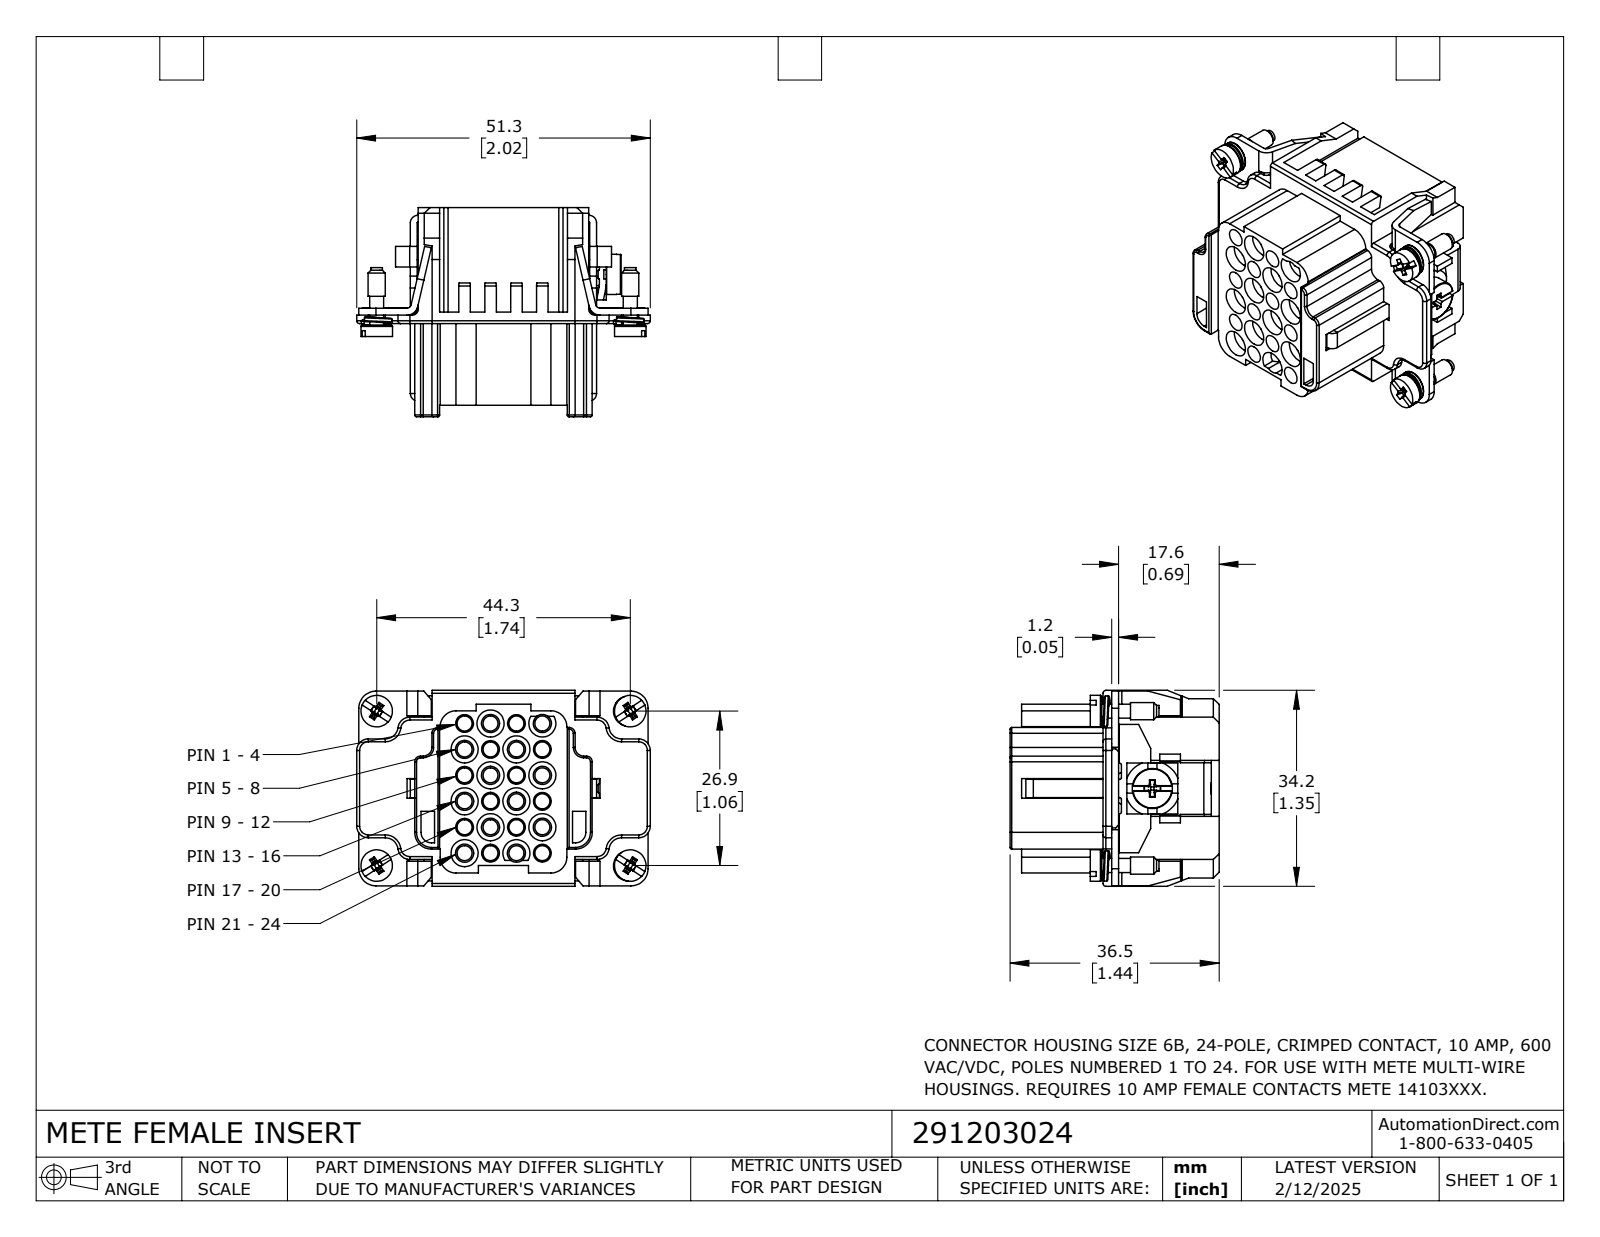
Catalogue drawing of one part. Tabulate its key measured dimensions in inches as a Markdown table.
| quantity | value |
| --- | --- |
| part name | 291203024 |
| STEP written by | SolidWorks 2024 (CONFIG_CONTROL_DESIGN) |
| units | inches |
| bodies | 13 solids, 1234 faces (660 planar, 469 cylindrical, 105 other) |
| overall size | 2.018 × 1.438 × 1.347 |
| volume | 1.254 in³ |
| surface area | 35.69 in² |
| round holes (diameter × count) | 0.103 × 24, 0.15 × 24, 0.139 × 21, 0.122 × 12, 0.125 × 12, 0.186 × 10, 0.114 × 4, 0.139 × 3, 0.142 × 2, 0.13 × 1 |
| round bosses / shafts (diameter × count) | 0.217 × 4, 0.209 × 4, 0.118 × 4, 0.096 × 4, 0.079 × 4, 0.126 × 2, 0.276 × 1, 0.201 × 1 |
| partial cylindrical surfaces (radius × count) | 0.01 × 32, 0.012 × 12, 0.004 × 10, 0.02 × 10, 0.051 × 10, 0.012 × 9, 0.006 × 8, 0.02 × 8 |
| main face-to-face distances | 0.047, 0.095, 0.075, 0.059, 0.054, 1.226, 1.233, 1.179, 0.194, 1.002 |
| hole center spacings | 0.398, 0.178, 0.356, 0.643, 0.535, 0.564, 0.178, 0.252 |
